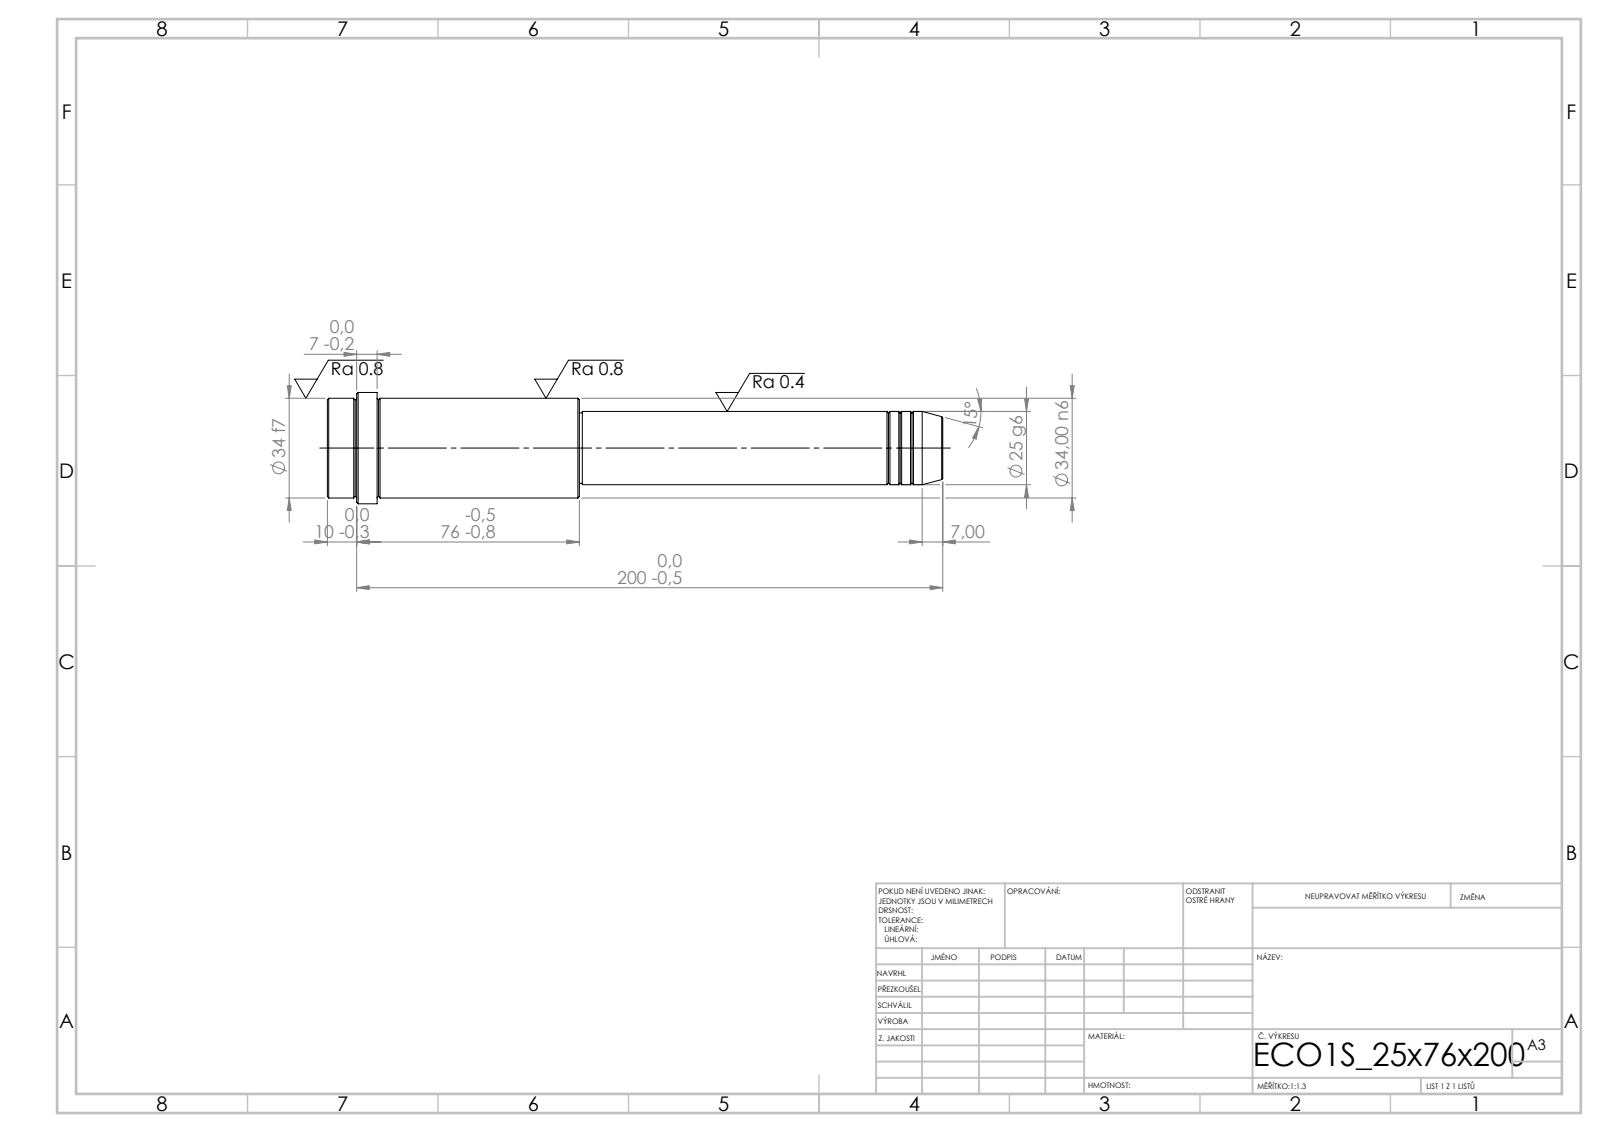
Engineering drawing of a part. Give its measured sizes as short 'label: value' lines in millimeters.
written by: SolidWorks 2019 (CONFIG_CONTROL_DESIGN)
unit: mm
bodies: 1 solid, 52 faces (6 planar, 16 cylindrical, 30 other)
size: 210 × 38 × 38
volume: 139 788 mm³; area: 21 330 mm²
bosses: 1× ⌀38, 1× ⌀34, 1× ⌀25, 1× ⌀24
face distances: 86, 124, 210, 193, 69, 17, 200, 76, 7, 10
